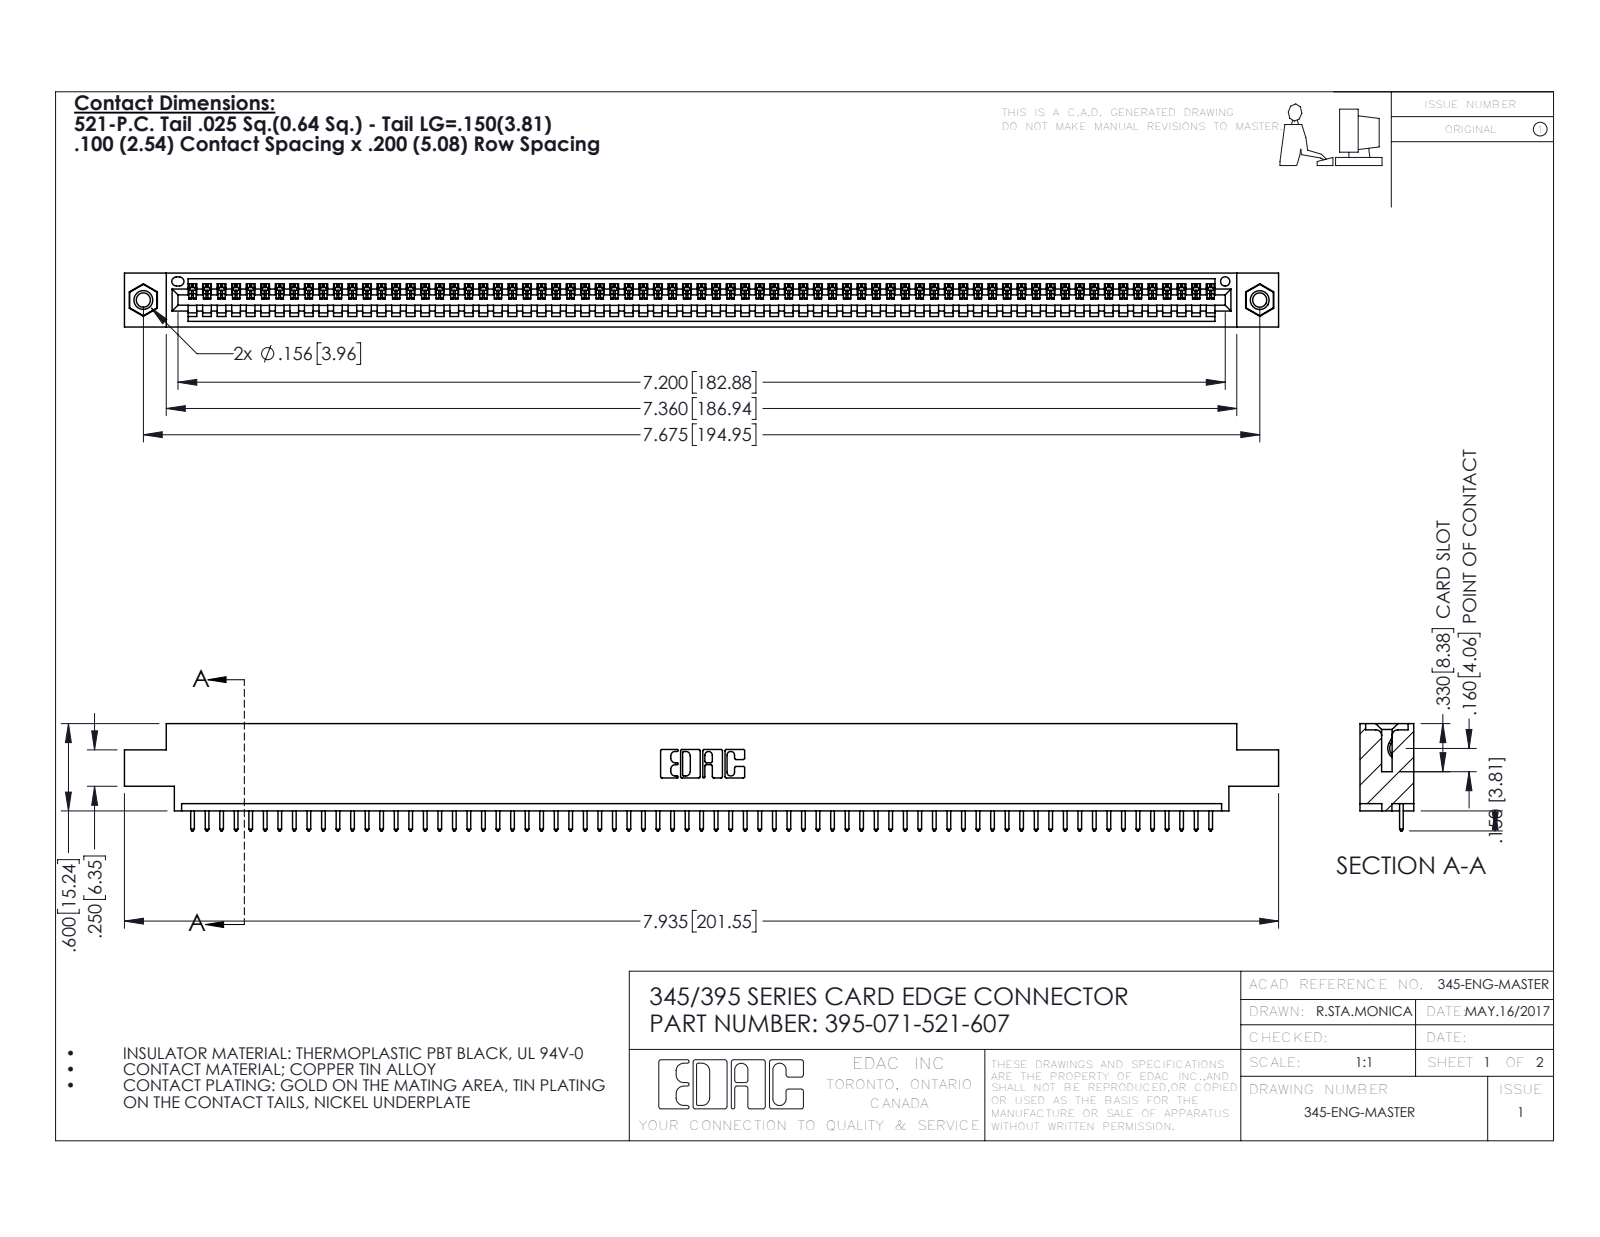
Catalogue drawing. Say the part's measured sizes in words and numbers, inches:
The part is named "395-071-521-607; 345-292-001_345-293-121; 345-250-001_345-250-005-103; 345 Part_0.170 Offset - 0.156 Dia-TI". Its 3-D file was written by "SolidWorks 2016 (CONFIG_CONTROL_DESIGN)". It is 74 solids with 4308 faces: 2956 planar, 1336 cylindrical and 16 other. Overall it measures 7.935 by 0.737 by 0.37 inches. Its volume is 1.163 cubic inches and its surface area 38.88 square inches. Round holes: 2 of diameter 0.098, 2 of diameter 0.125, 2 of diameter 0.156, 1 of diameter 0.064. Round bosses or shafts: 2 of diameter 0.155. Partial cylindrical surfaces (rounded edges, fillets, slot ends): 142 of radius 0.006, 142 of radius 0.01, 22 of radius 0.01, 6 of radius 0.007, 6 of radius 0.031, 3 of radius 0.026, 2 of radius 0.031, 2 of radius 0.04. The main face-to-face distances are 0.072, 0.298, 0.37, 0.2, 0.098, 0.272, 0.025, 0.225, 0.175, 0.149. The hole center spacings are 0.27, 7.439, 7.675.
